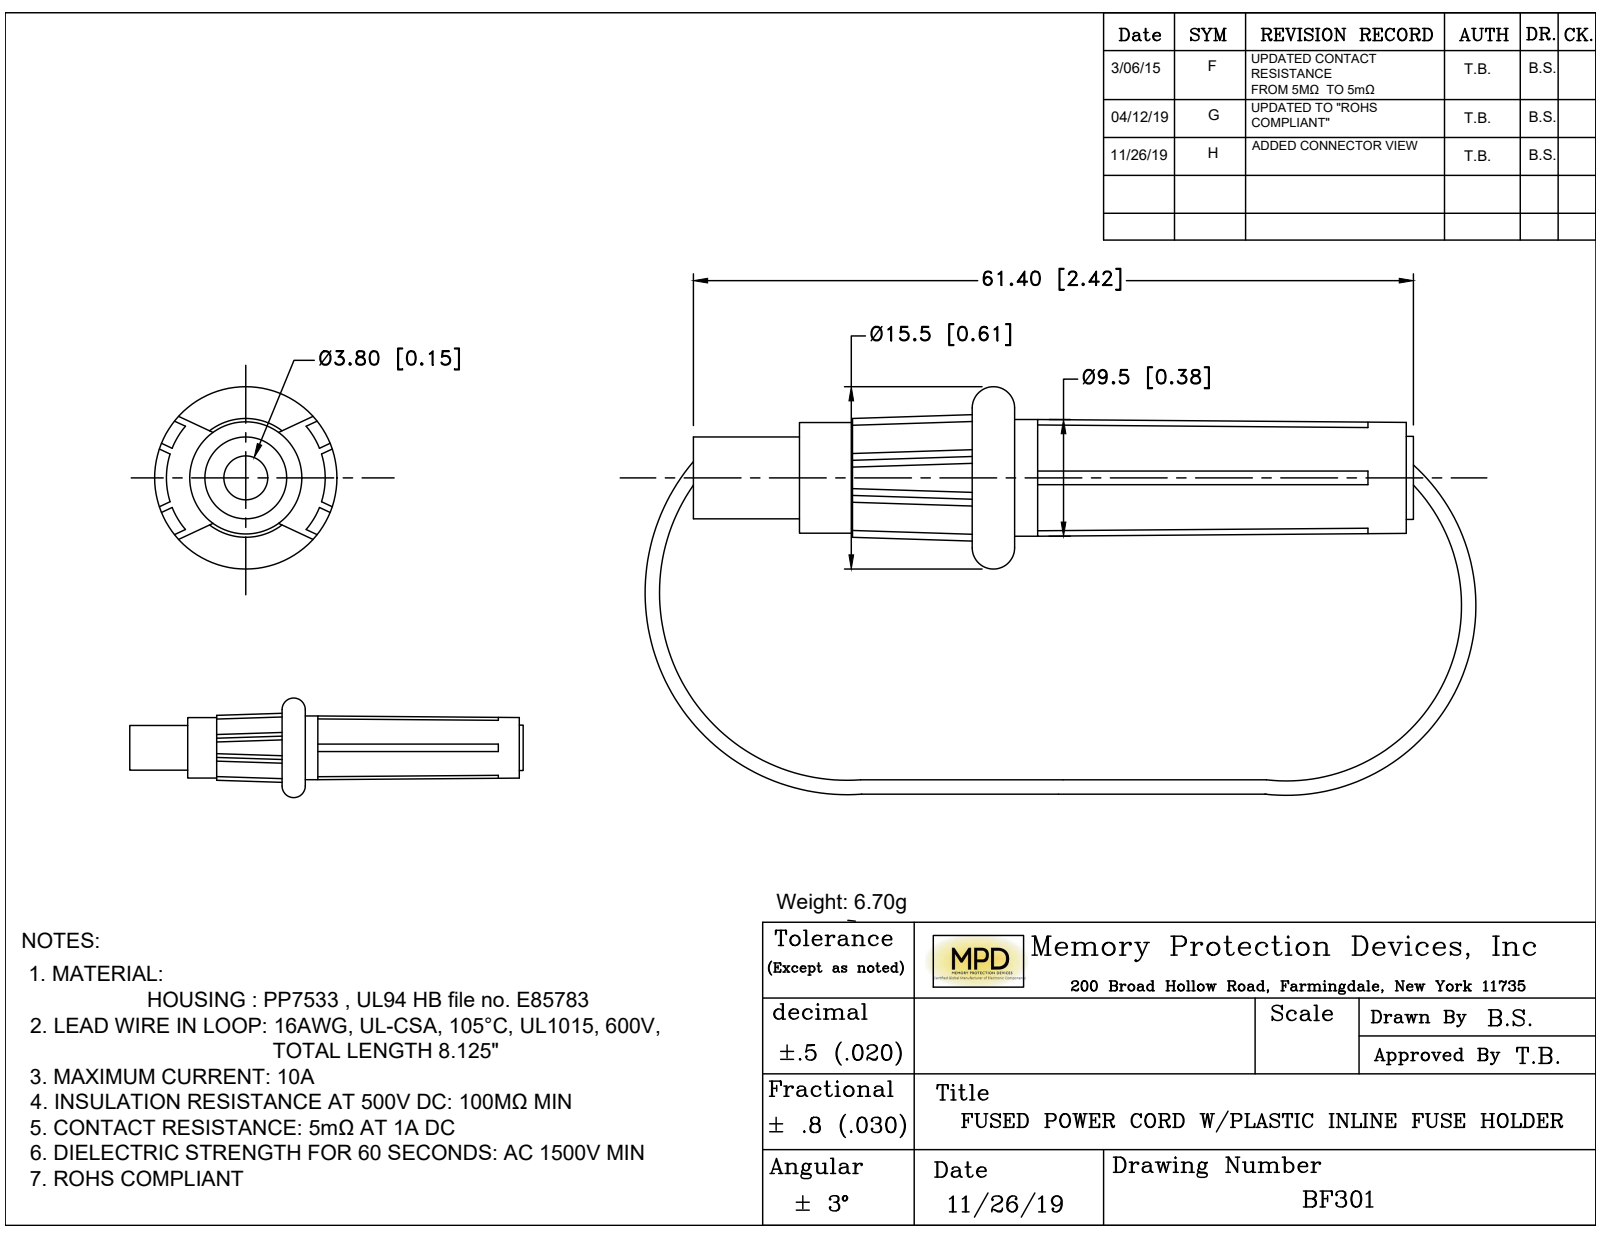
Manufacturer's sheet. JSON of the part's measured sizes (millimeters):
{"part_name": "BF301", "step_written_by": "SolidWorks 2017 (AUTOMOTIVE_DESIGN)", "units": "millimeters", "bodies": {"solids": 2, "faces": 110, "planar": 54, "cylindrical": 22, "other": 34}, "overall_size": [79.93, 32.47, 15.5], "volume_mm3": 4391, "surface_area_mm2": 3376, "round_holes": [[3.8, 1], [7.89, 1]], "round_bosses_or_shafts": [[1.5, 2], [9.5, 1], [7.69, 1], [7, 1]], "face_to_face_distances": [0.5, 2.7, 3.6, 3.2, 2.2, 14.77, 18.37, 2, 9.03, 23.8]}
